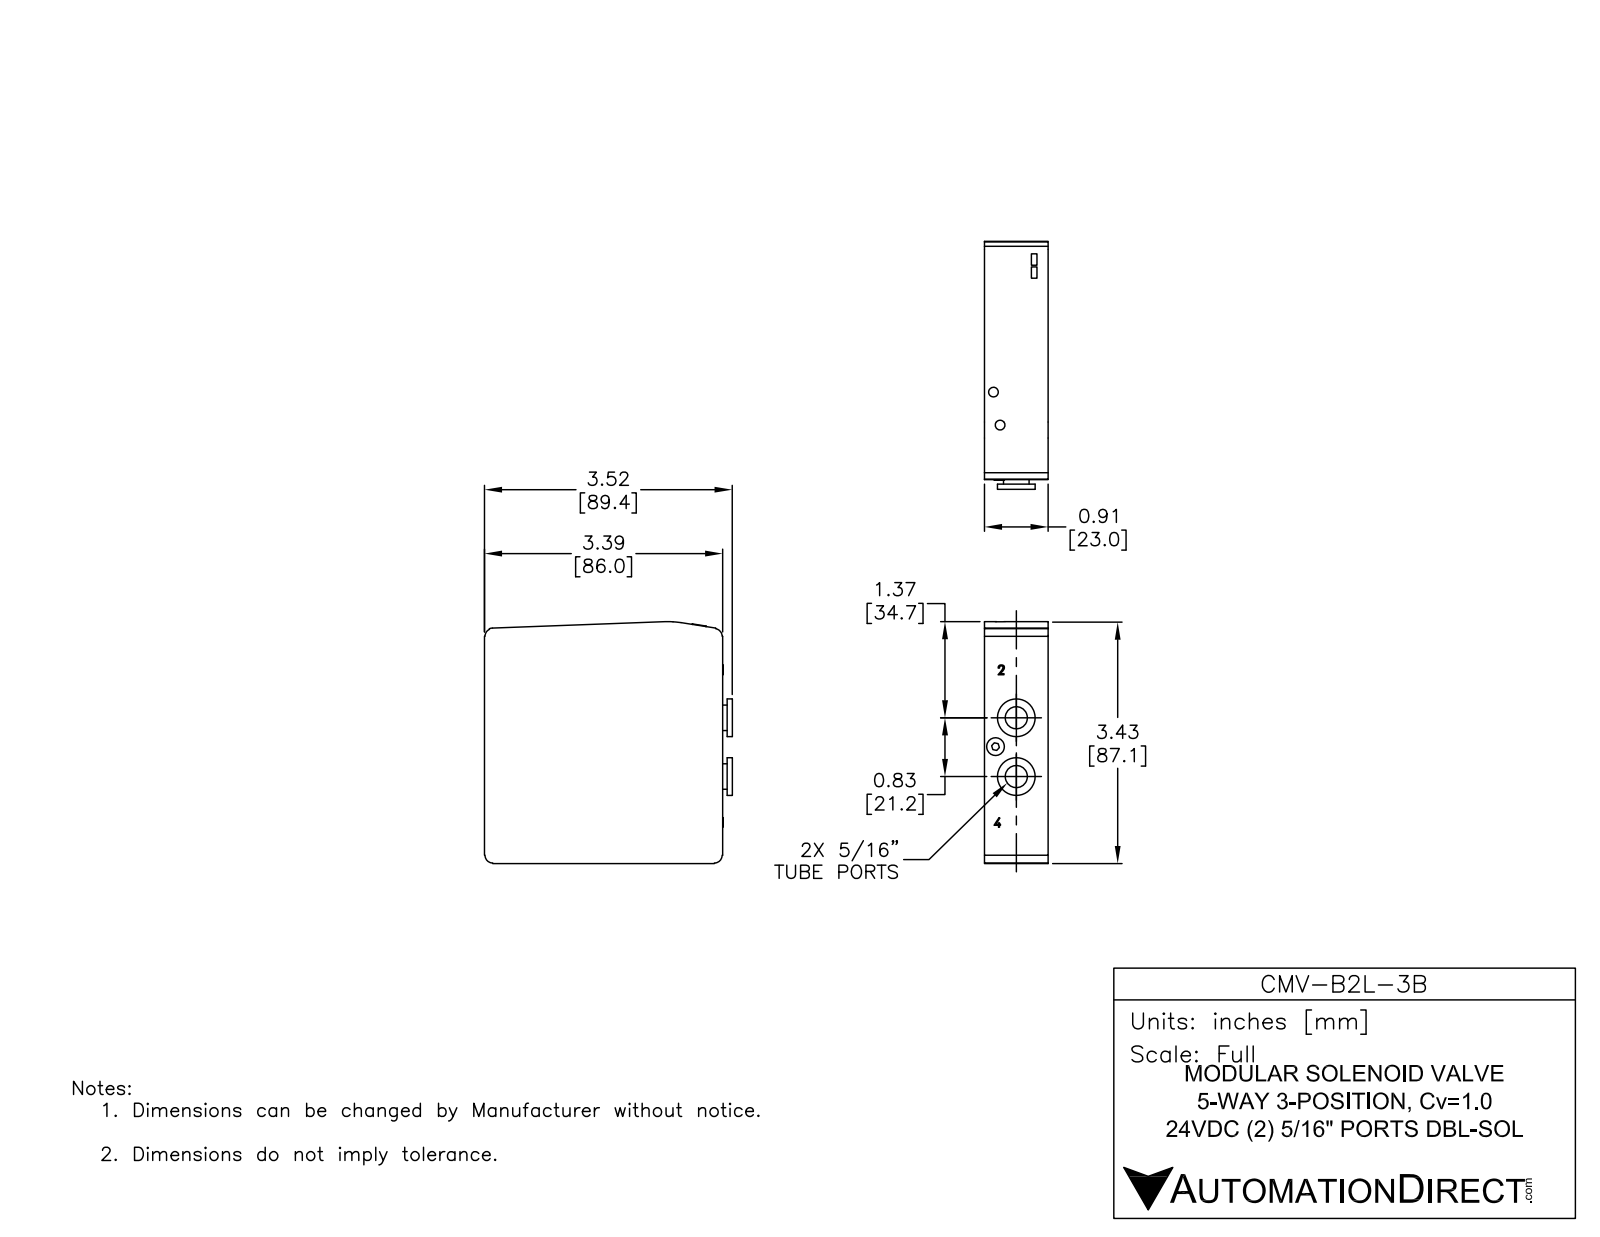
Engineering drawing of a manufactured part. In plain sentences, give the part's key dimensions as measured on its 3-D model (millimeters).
The part is named "CMV-B2L-3B". Its 3-D file was written by "SolidWorks 2013 (AUTOMOTIVE_DESIGN)". It is 75 solids with 1173 faces: 883 planar, 162 cylindrical and 128 other. Overall it measures 89.5 by 87.3 by 31.43 millimeters. Its volume is 154 040 cubic millimeters and its surface area 54 389 square millimeters. Round holes: 4 of diameter 4.4, 4 of diameter 5.25, 2 of diameter 3.35, 2 of diameter 6.5, 2 of diameter 9.75, 2 of diameter 14, 2 of diameter 18, 1 of diameter 3.6, 1 of diameter 6.25. Round bosses or shafts: 4 of diameter 4, 4 of diameter 1.5, 2 of diameter 15.25, 2 of diameter 11, 2 of diameter 6.25, 2 of diameter 5.75, 2 of diameter 4.2, 1 of diameter 3.5. Partial cylindrical surfaces (rounded edges, fillets, slot ends): 12 of radius 2.35, 4 of radius 0.78, 4 of radius 1.5, 4 of radius 2.8, 2 of radius 0.15, 2 of radius 0.25, 2 of radius 1, 2 of radius 2.25. The main face-to-face distances are 22.5, 12.5, 10, 83, 3, 1, 65.12, 50.25, 32.75, 53.25. The hole center spacings are 9.7, 11.99, 12.17, 16, 22.17, 31.45, 31.52, 39.5.
